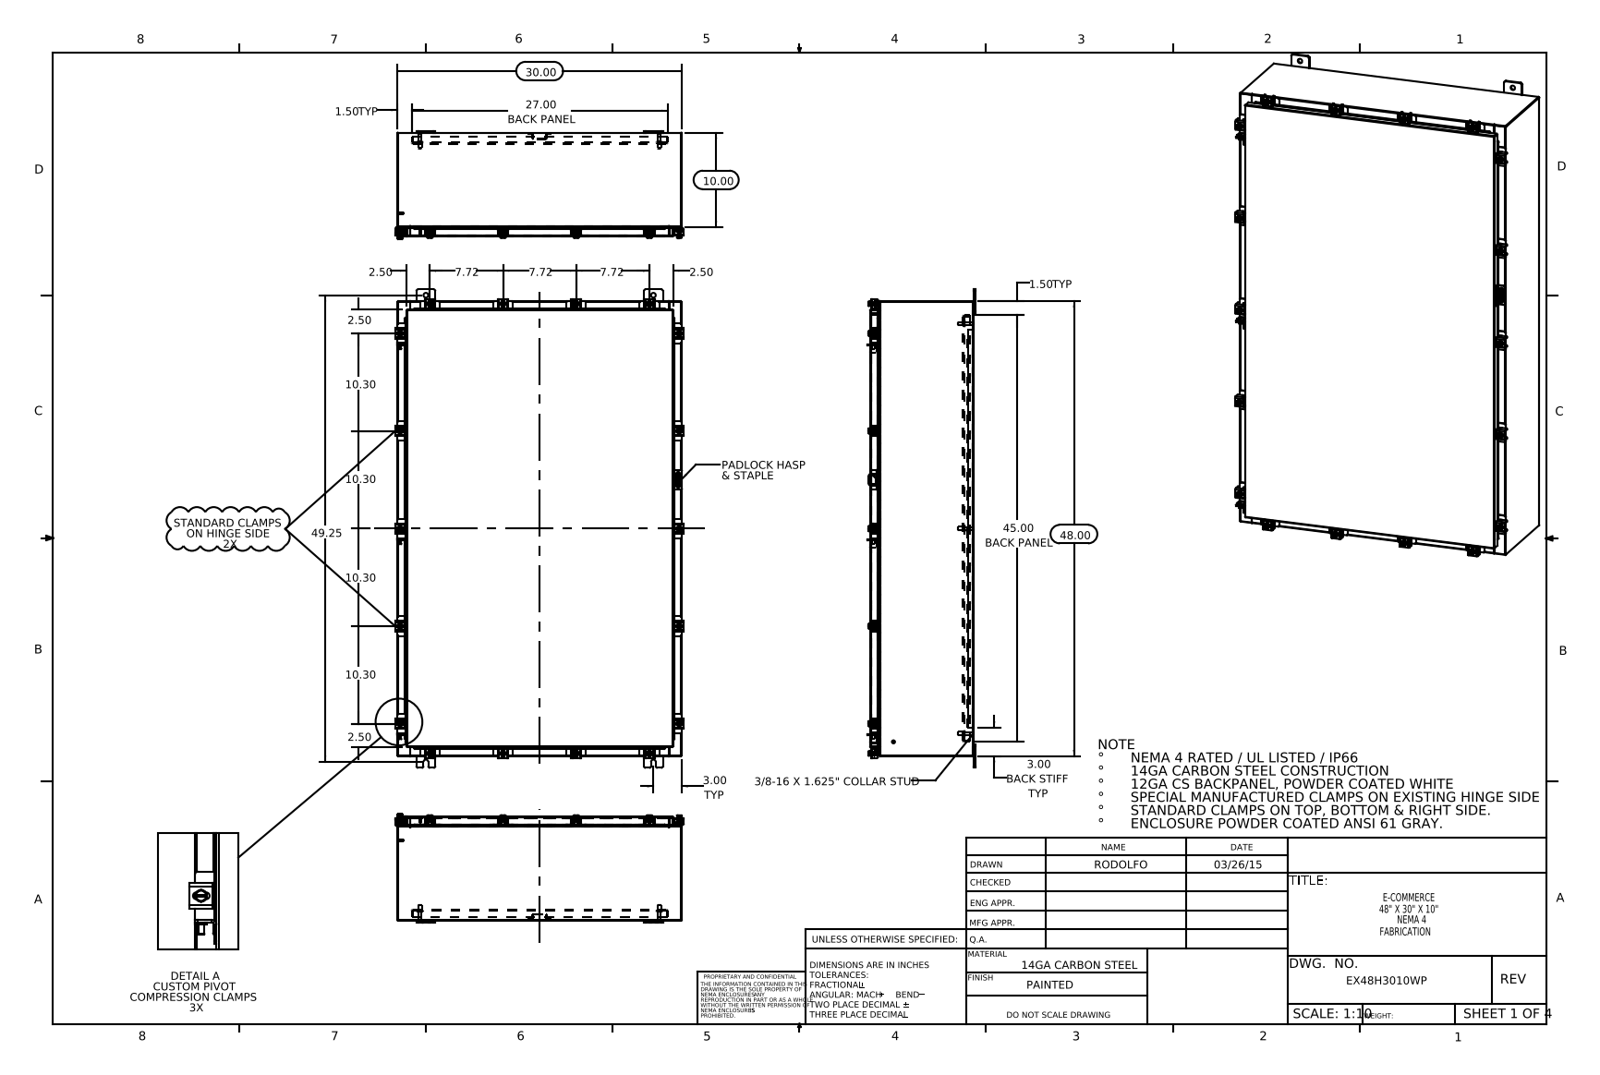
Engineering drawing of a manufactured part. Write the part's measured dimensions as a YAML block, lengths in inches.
part_name: "22104005_DEFAULT_RTP30; EX48H3010WP Cover; HW-CLN-NH-20330; EX48H3010WP Clamp Assembly (+8 more)"
step_written_by: "SolidWorks 2014 (CONFIG_CONTROL_DESIGN)"
units: inches
bodies: {solids: 116, faces: 2878, planar: 1525, cylindrical: 1123, other: 230}
overall_size: [50.5, 30.421, 11.453]
volume: 516.4
surface_area: 12799
round_holes:
  - {diameter: 0.213, count: 18}
  - {diameter: 0.26, count: 18}
  - {diameter: 0.5, count: 10}
  - {diameter: 0.125, count: 1}
  - {diameter: 0.25, count: 1}
round_bosses_or_shafts:
  - {diameter: 0.5, count: 18}
  - {diameter: 0.25, count: 18}
  - {diameter: 0.399, count: 15}
  - {diameter: 0.625, count: 6}
  - {diameter: 0.375, count: 6}
  - {diameter: 0.33, count: 6}
  - {diameter: 0.315, count: 2}
  - {diameter: 0.236, count: 2}
partial_cylinders:
  - {radius: 0.06, count: 76}
  - {radius: 0.141, count: 36}
  - {radius: 0.12, count: 33}
  - {radius: 0.013, count: 30}
  - {radius: 0.09, count: 27}
  - {radius: 0.088, count: 26}
  - {radius: 0.05, count: 25}
  - {radius: 0.145, count: 24}
face_to_face_distances: [0.075, 10.9, 10.826, 10.975, 0.104, 1, 1.075, 9.826, 9.9, 1.179]
hole_center_spacings: [31.2, 29.451, 2.347, 4.44, 10.298, 20.701, 21.625, 23.749]
